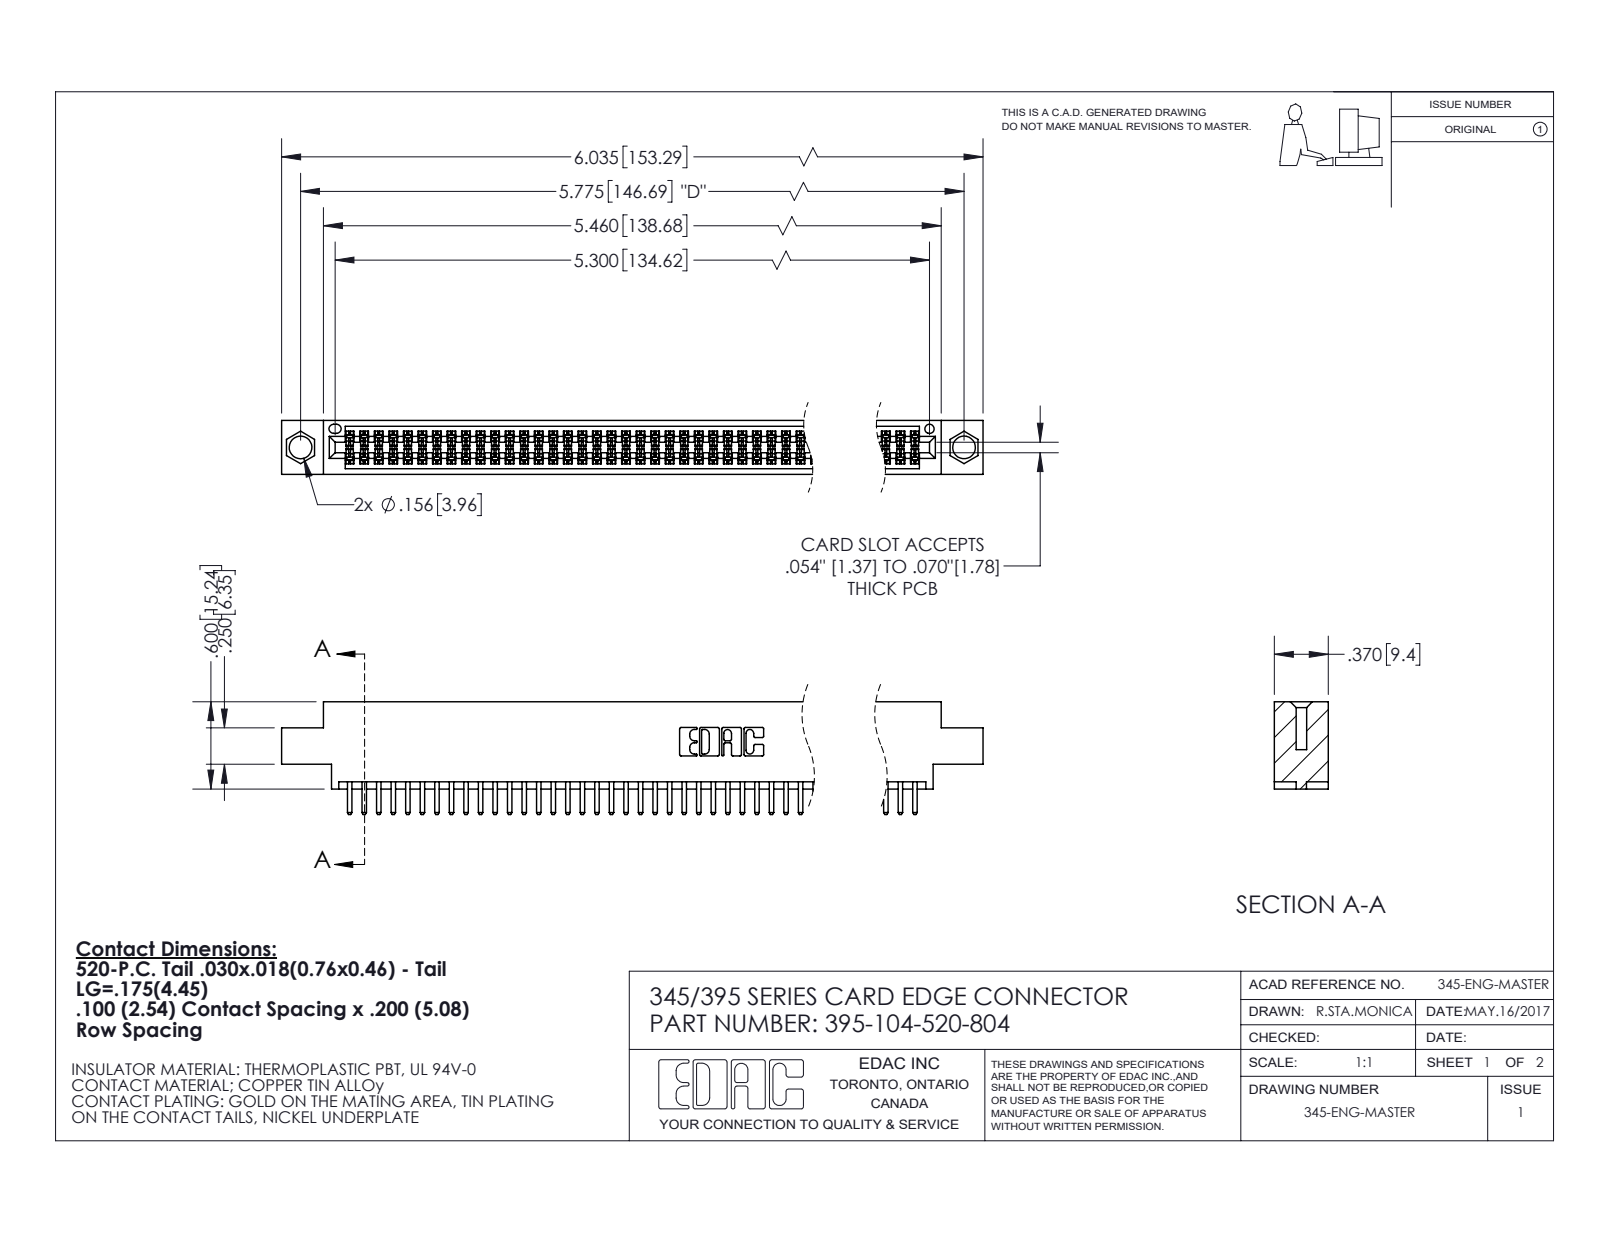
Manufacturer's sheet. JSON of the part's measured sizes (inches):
{"part_name": "395-104-520-804; 345 Part_0.170 Offset - 0.156 Dia-TI; 345-292-001_345-293-120", "step_written_by": "SolidWorks 2020 (CONFIG_CONTROL_DESIGN)", "units": "inches", "bodies": {"solids": 105, "faces": 5760, "planar": 3738, "cylindrical": 2022, "other": 0}, "overall_size": [6.035, 0.775, 0.37], "volume_in3": 0.898, "surface_area_in2": 33.86, "round_holes": [[0.156, 2], [0.064, 1]], "partial_cylinders_radius": [[0.006, 156], [0.01, 108], [0.01, 22], [0.007, 6], [0.031, 6], [0.026, 3], [0.014, 2], [0.019, 2]], "face_to_face_distances": [0.072, 0.298, 0.2, 0.37, 0.098, 0.272, 0.025, 0.225, 0.022, 0.072], "hole_center_spacings": [0.27, 5.539, 5.775]}
